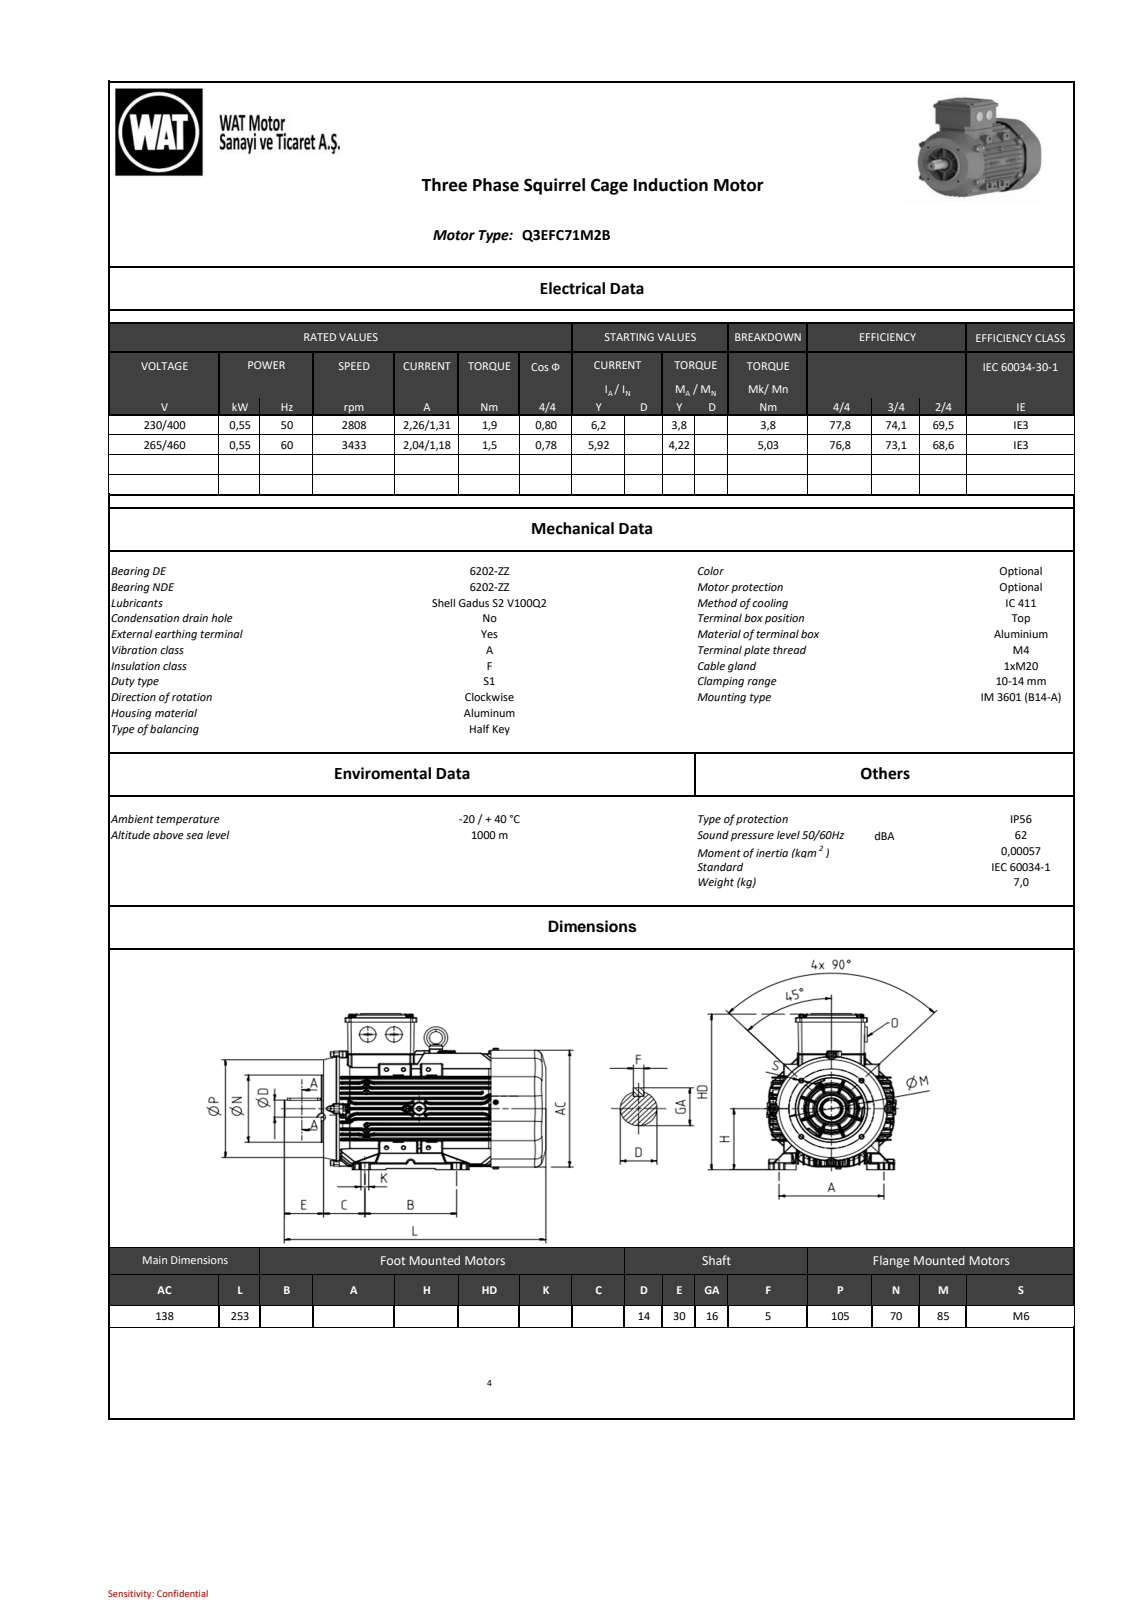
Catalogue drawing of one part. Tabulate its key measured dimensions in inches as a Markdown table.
| quantity | value |
| --- | --- |
| part name | 001_objects |
| STEP written by | SIEMENS PLM Software NX2206.8101 (AUTOMOTIVE_DESIGN) |
| units | inches |
| bodies | 0 solids, 2792 faces (1401 planar, 707 cylindrical, 684 other) |
| overall size | 9.921 × 6.933 × 5.433 |
| round holes (diameter × count) | 0.13 × 9, 0.144 × 8, 0.118 × 7, 0.098 × 6, 0.197 × 5, 0.177 × 4, 0.183 × 4, 0.189 × 4, 0.146 × 3, 0.181 × 2, 0.236 × 1, 0.26 × 1 |
| round bosses / shafts (diameter × count) | 0.315 × 8, 0.157 × 8, 0.472 × 4, 0.13 × 4, 5.433 × 1, 5.354 × 1, 2.756 × 1, 2.402 × 1 |
| partial cylindrical surfaces (radius × count) | 0.039 × 97, 0.02 × 51, 0.047 × 36, 0.059 × 28, 0.079 × 19, 0.157 × 17, 0.128 × 16, 0.004 × 14 |
| main face-to-face distances | 0.079, 0.118, 0.039, 1.378, 3.268, 0.157, 7.185, 7.303, 6.083, 0.197 |
| hole center spacings | 2.417, 2.165, 1.441, 2.645, 2.646, 2.362, 0.339, 1.467 |
